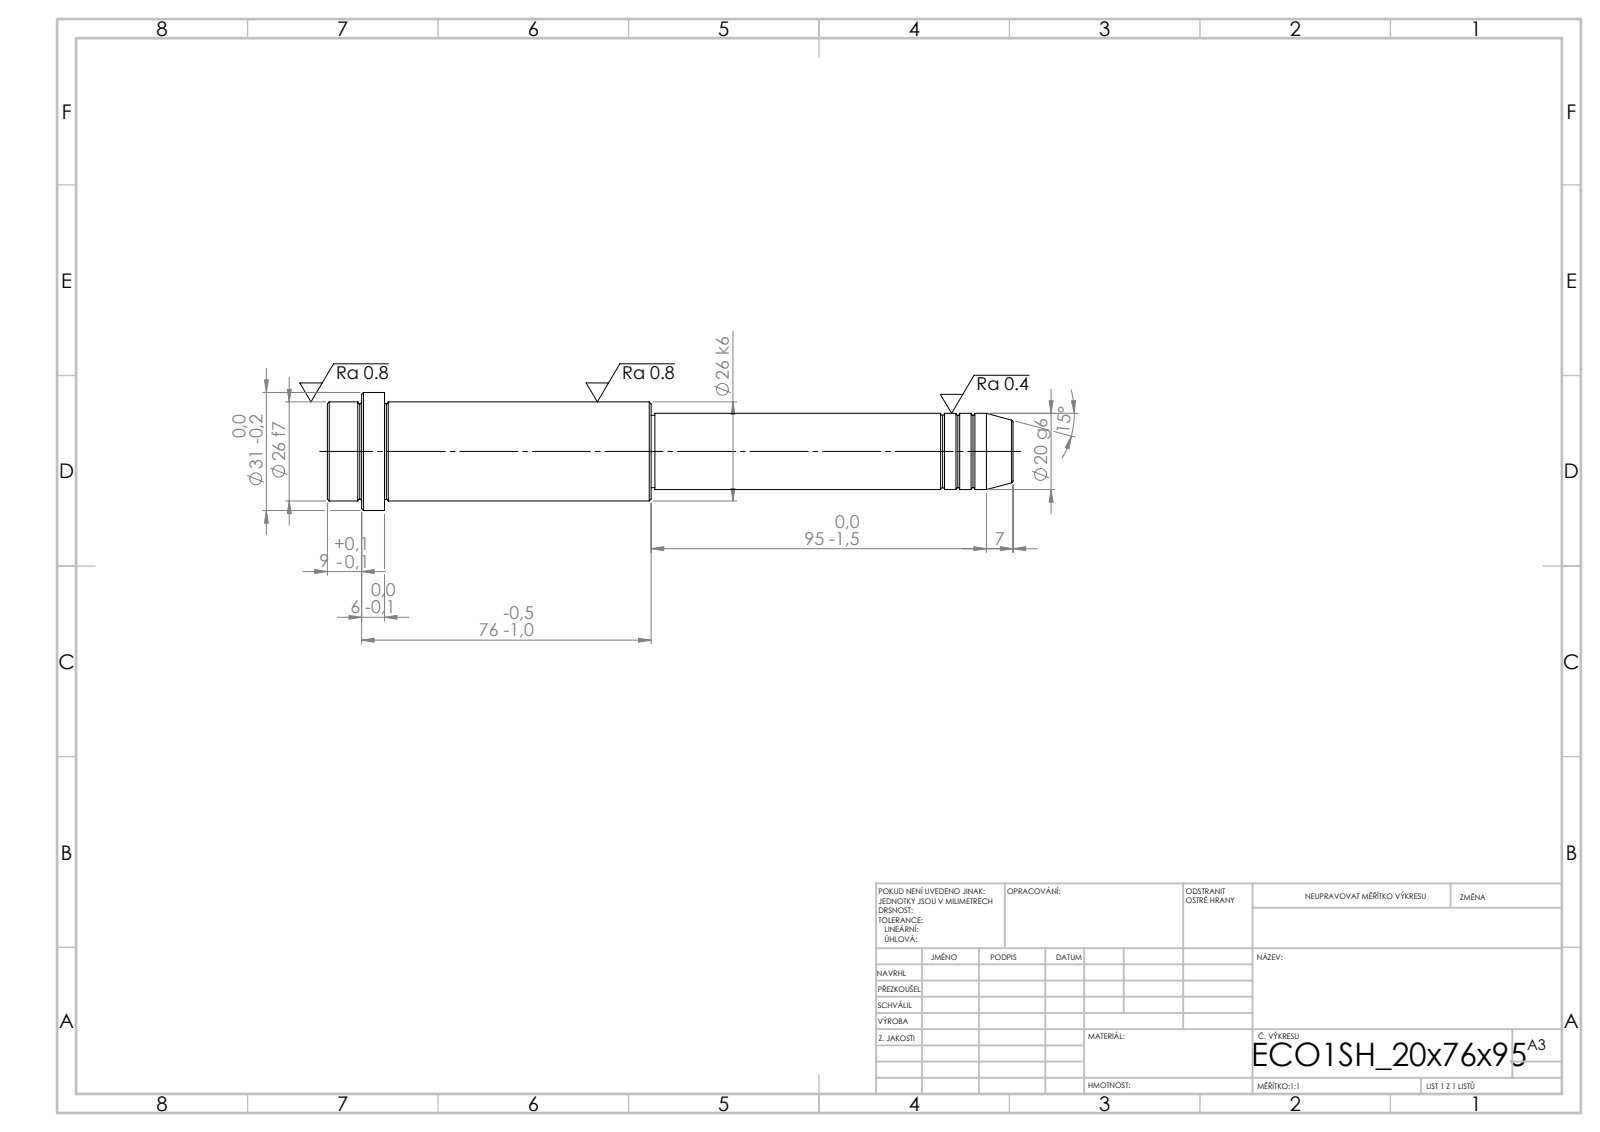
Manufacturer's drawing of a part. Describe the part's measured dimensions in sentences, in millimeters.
Its 3-D file was written by "SolidWorks 2019 (CONFIG_CONTROL_DESIGN)". It is 1 solid with 52 faces: 6 planar, 16 cylindrical and 30 other. Overall it measures 180 by 31 by 31 millimeters. Its volume is 75 731 cubic millimeters and its surface area 14 542 square millimeters. Round bosses or shafts: 1 of diameter 31, 1 of diameter 26, 1 of diameter 20, 1 of diameter 19. The main face-to-face distances are 15, 70, 85, 95, 165, 180, 171, 76, 6, 9.
